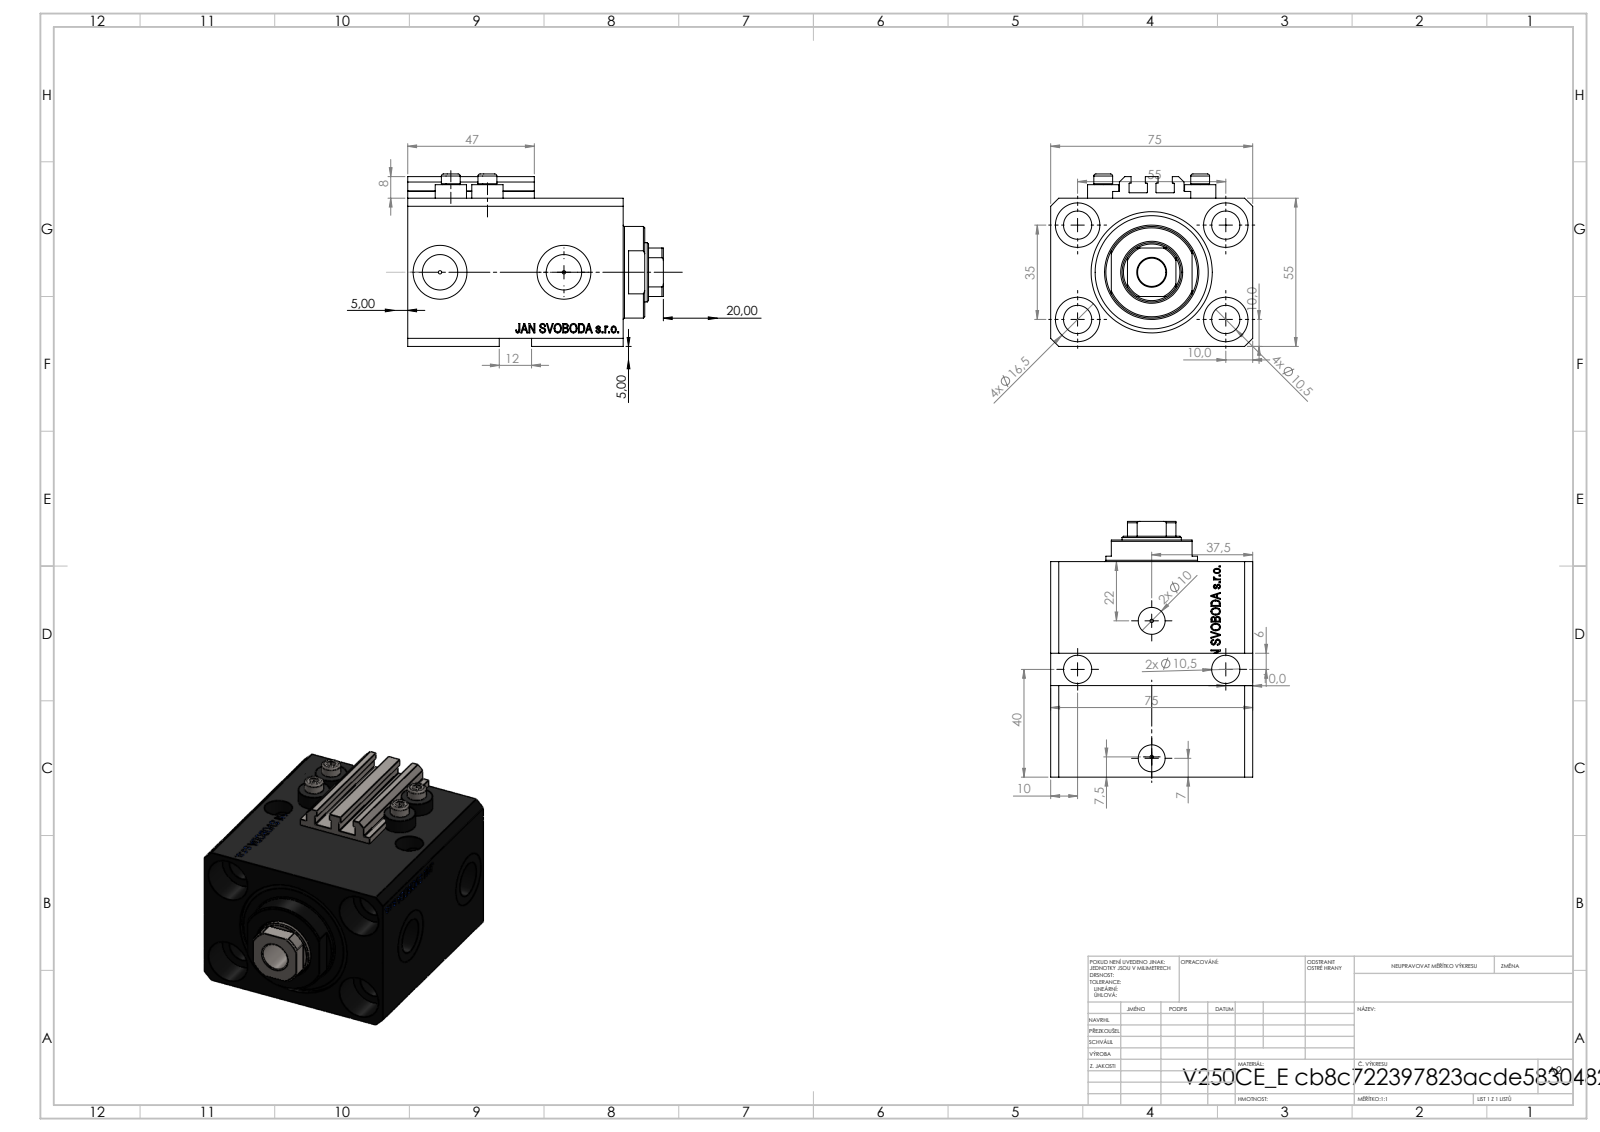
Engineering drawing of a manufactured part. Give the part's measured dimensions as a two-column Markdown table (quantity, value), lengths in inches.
| quantity | value |
| --- | --- |
| part name | V250CE_VC_E; V250CE_C_VCP; ALLEN BOLT V250CE; V250CE_E_Body |
| STEP written by | SolidWorks 2019 (CONFIG_CONTROL_DESIGN) |
| units | inches |
| bodies | 8 solids, 1080 faces (518 planar, 138 cylindrical, 424 other) |
| overall size | 3.74 × 2.953 × 2.52 |
| volume | 17.1 in³ |
| surface area | 117.2 in² |
| round holes (diameter × count) | 0.413 × 7, 0.049 × 4, 0.157 × 4, 0.65 × 4, 0.394 × 2, 0.518 × 2, 0.787 × 2, 0.866 × 1, 1.26 × 1, 1.772 × 1 |
| round bosses / shafts (diameter × count) | 0.457 × 4, 0.276 × 4, 1.339 × 1 |
| partial cylindrical surfaces (radius × count) | 0.008 × 10, 0.413 × 1 |
| main face-to-face distances | 2.165, 2.953, 0.591, 3.15, 2.559, 0.118, 0.39, 2.169, 2.76, 2.126 |
| hole center spacings | 1.283, 2.165, 0.535, 0.555, 0.783, 0.792, 1.016, 1.121 |
